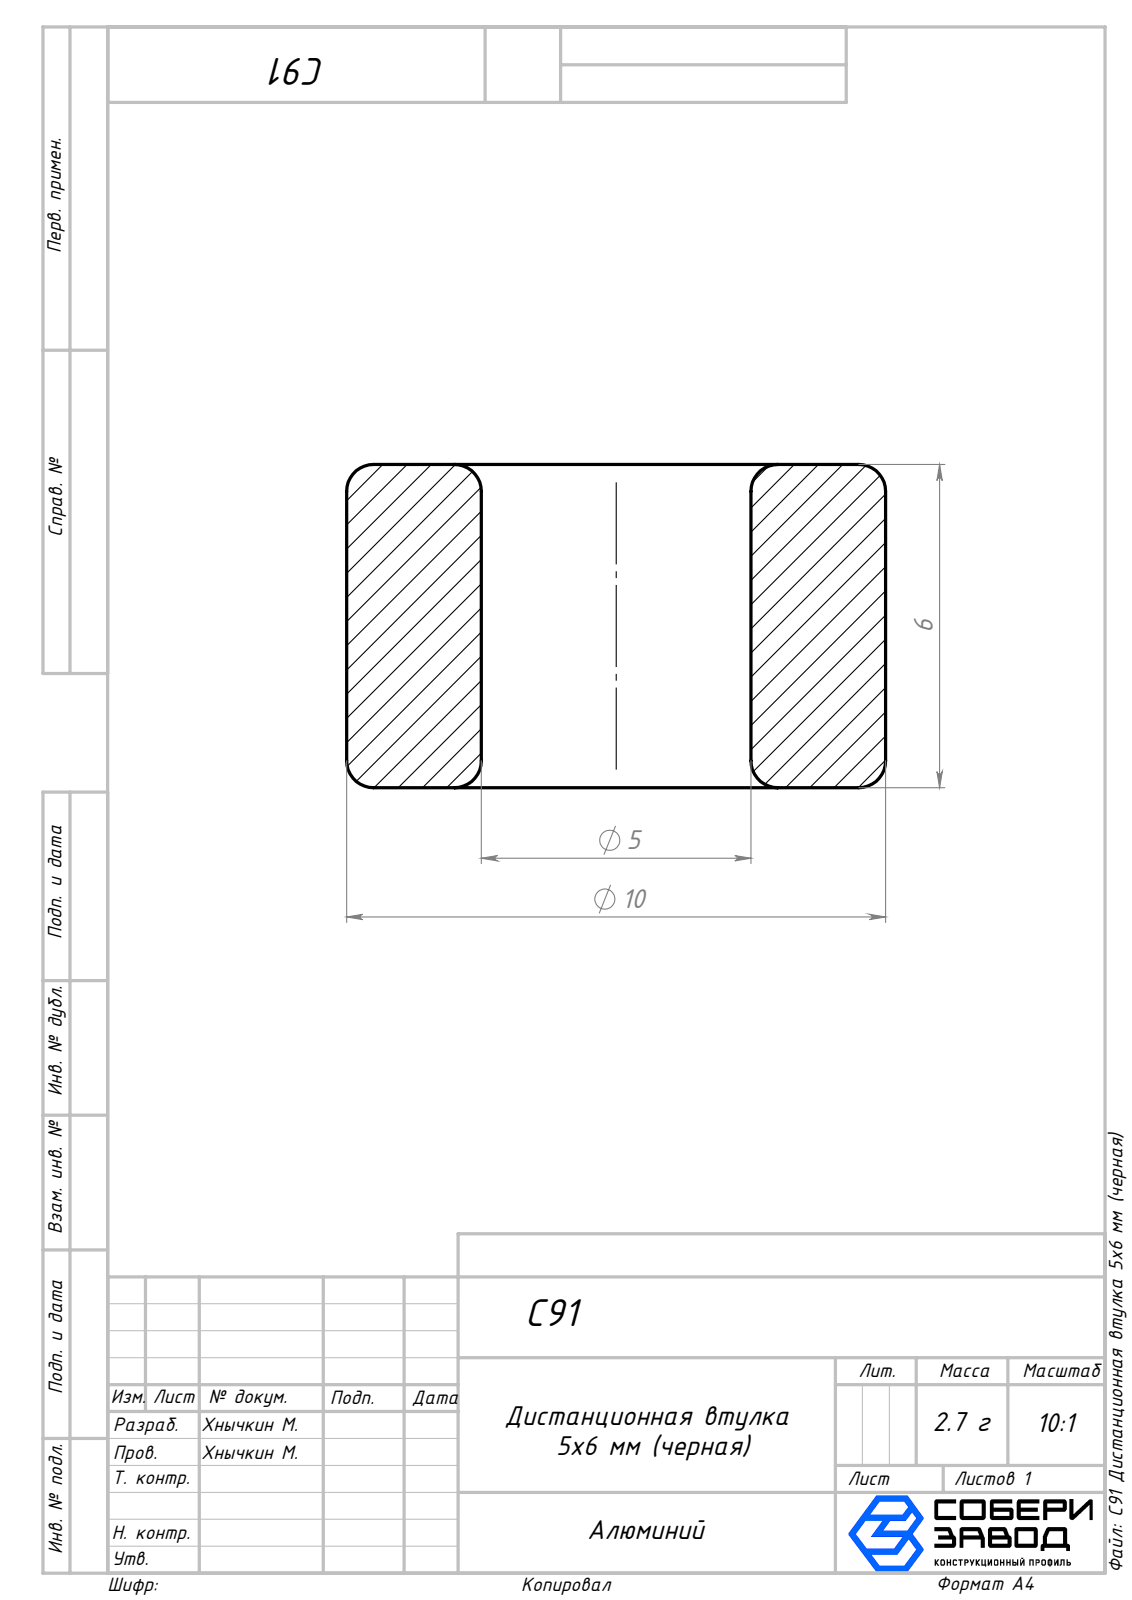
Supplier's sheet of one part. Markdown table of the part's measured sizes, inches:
| quantity | value |
| --- | --- |
| part name | C91 Дистанционная втулка 5х6 мм (черная) |
| STEP written by | SolidWorks 2026 (AUTOMOTIVE_DESIGN) |
| units | inches |
| bodies | 1 solid, 14 faces (2 planar, 4 cylindrical, 8 other) |
| overall size | 0.394 × 0.394 × 0.236 |
| volume | 0.021 in³ |
| surface area | 0.589 in² |
| round holes (diameter × count) | 0.197 × 1 |
| round bosses / shafts (diameter × count) | 0.394 × 1 |
| main face-to-face distances | 0.236 |
